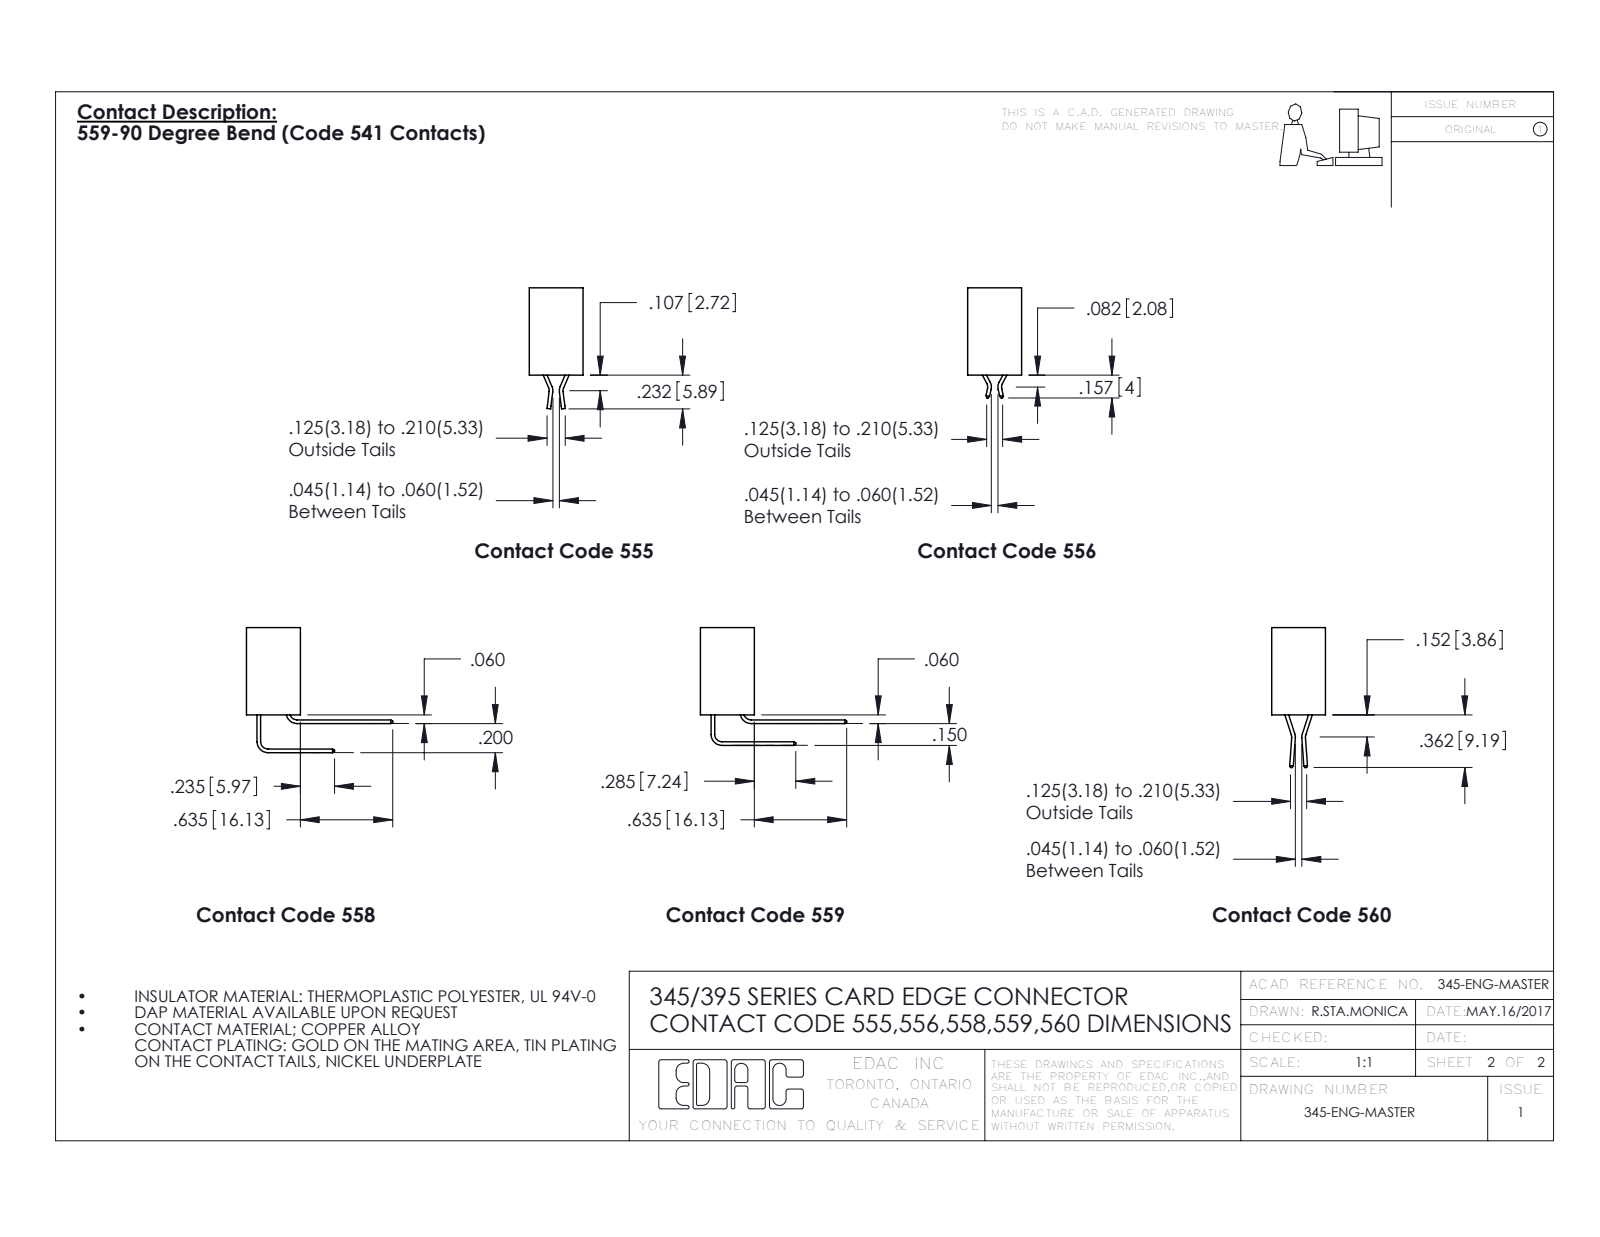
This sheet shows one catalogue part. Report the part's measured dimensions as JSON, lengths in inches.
{"part_name": "345-292-001_555 Tail; 395-026-555-512; 345 Part_0.110 Offset - Side Mount", "step_written_by": "SolidWorks 2016 (CONFIG_CONTROL_DESIGN)", "units": "inches", "bodies": {"solids": 27, "faces": 1586, "planar": 890, "cylindrical": 696, "other": 0}, "overall_size": [2.135, 0.832, 0.37], "volume_in3": 0.3, "surface_area_in2": 10.73, "round_holes": [[0.128, 2], [0.064, 1]], "partial_cylinders_radius": [[0.016, 65], [0.02, 52], [0.006, 39], [0.01, 22], [0.007, 6], [0.031, 6], [0.026, 3], [0.01, 2]], "face_to_face_distances": [0.298, 0.072, 0.2, 0.37, 0.025, 0.098, 0.272, 0.225, 0.1, 0.16], "hole_center_spacings": [1.875]}
